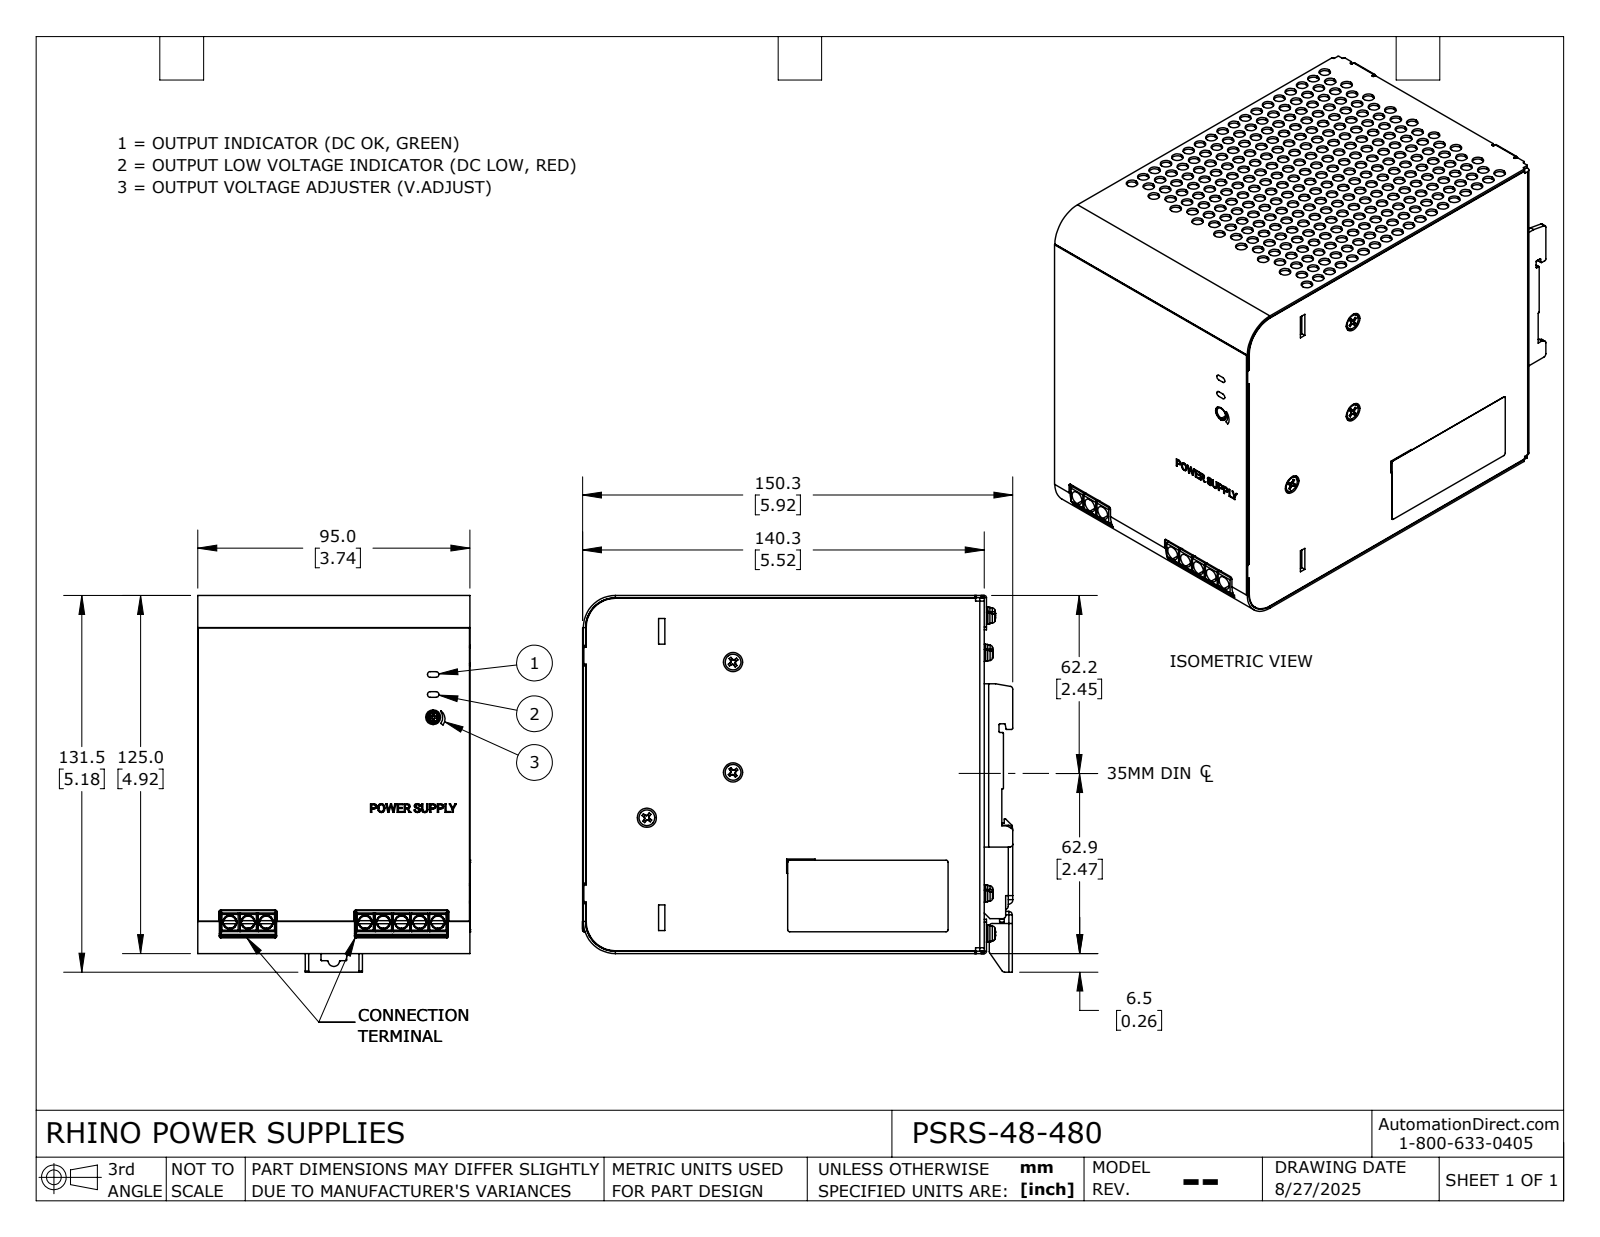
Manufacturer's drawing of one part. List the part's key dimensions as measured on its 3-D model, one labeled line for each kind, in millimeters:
Part name (STEP PRODUCT): PSRS-48-480
STEP written by: SolidWorks 2024 (AUTOMOTIVE_DESIGN)
Units: millimetres
Bodies: 4 solids, 4312 faces (1983 planar, 1867 cylindrical, 462 other)
Overall size (bounding box): 150.25 × 131.5 × 95.05
Volume: 1 662 000 mm³ · Surface area: 127 300 mm²
Round holes (diameter × count): ⌀4 ×304, ⌀3.1 ×16, ⌀3.5 ×16, ⌀3.6 ×13, ⌀2.5 ×8, ⌀3 ×8, ⌀3.8 ×8, ⌀4.65 ×8, ⌀4.85 ×8, ⌀6.7 ×4, ⌀1.5 ×1, ⌀3.4 ×1
Round bosses / shafts (diameter × count): ⌀3 ×22, ⌀6 ×16, ⌀5.9 ×16, ⌀4.75 ×8, ⌀2.96 ×8, ⌀5.5 ×4
Partial cylindrical surfaces — rounded edges, fillets, slot ends (radius × count): R0.3 ×61, R0.5 ×29, R1 ×28, R0.15 ×18, R1.6 ×17, R1.2 ×13, R0.1 ×9, R0.6 ×2
Main face-to-face distances: 95, 140.25, 0.8, 124.2, 125, 1.6, 123.4, 141.85, 8.4, 10
Hole centre spacings: 5.6, 12.17, 22.31, 10.8, 11.2, 21.6, 32.88, 15.56
